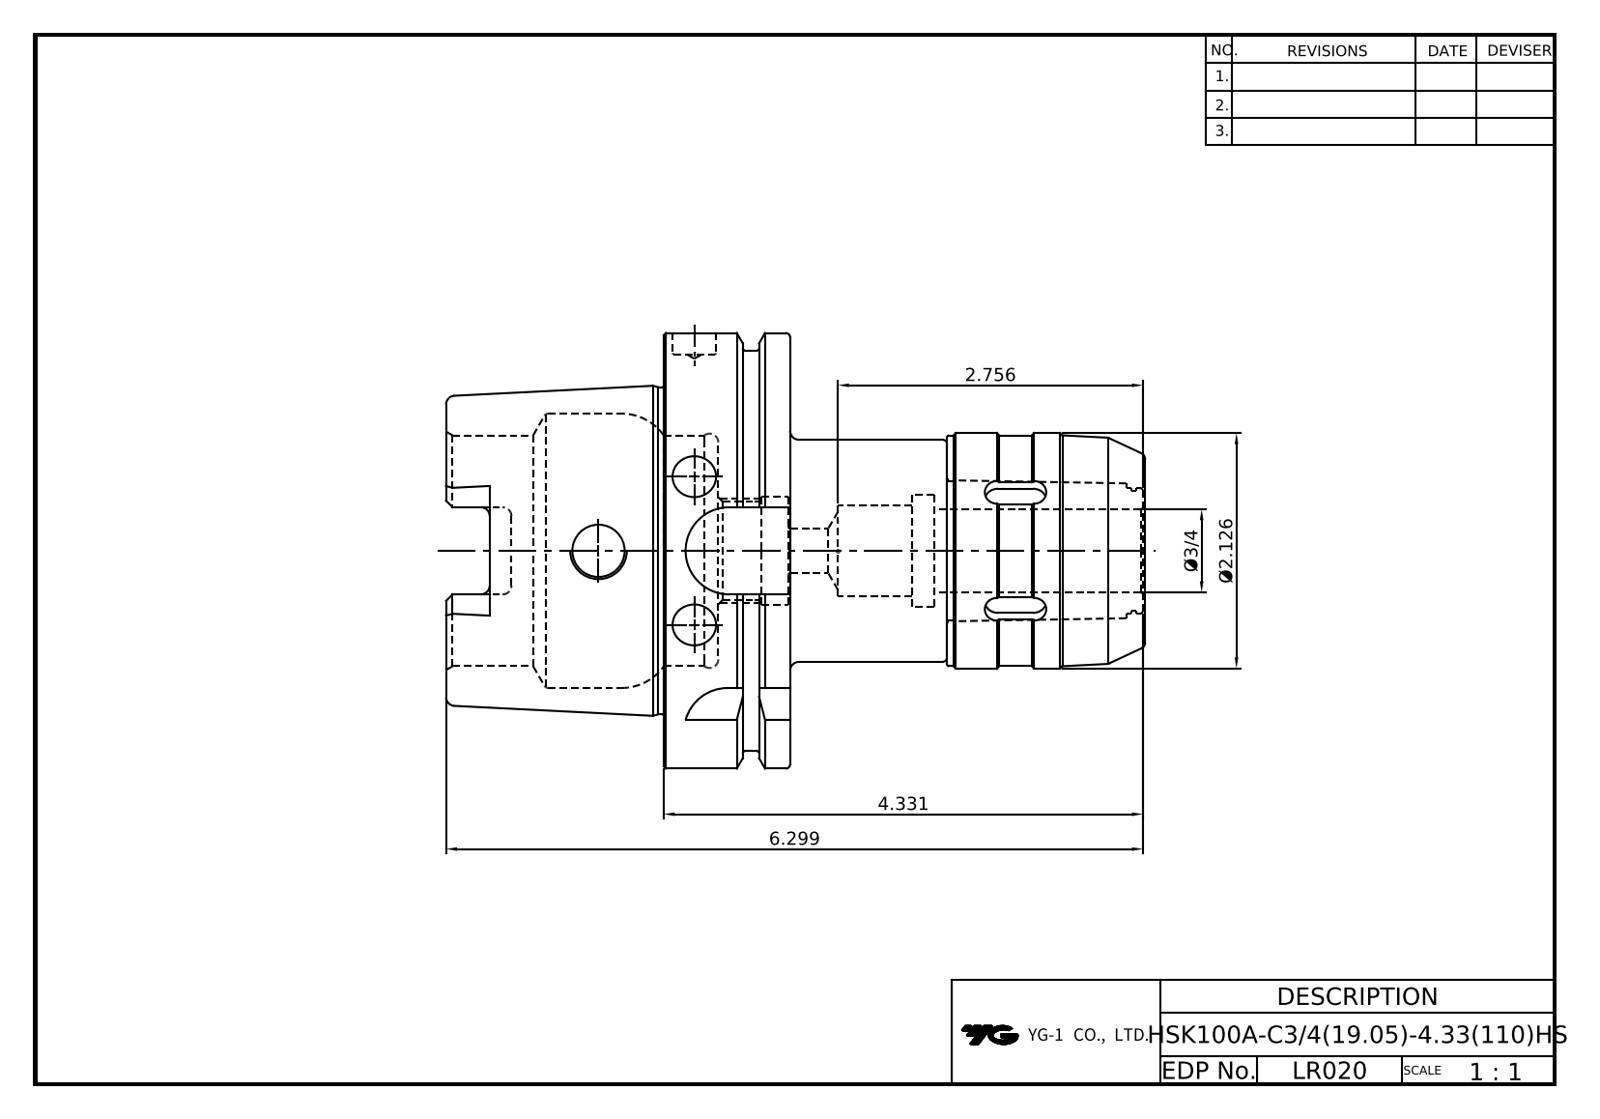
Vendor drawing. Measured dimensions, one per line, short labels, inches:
name: HSK100A-C19.05-110HS; C20-CAP
written by: Autodesk Inventor 2020 (AUTOMOTIVE_DESIGN)
unit: in
bodies: 2 solids, 207 faces (67 planar, 63 cylindrical, 77 other)
size: 6.319 × 3.937 × 3.937
volume: 23.8 in³; area: 124.4 in²
holes: 2× ⌀0.394, 2× ⌀0.472, 1× ⌀0.75, 1× ⌀0.827, 1× ⌀0.881, 1× ⌀0.984, 1× ⌀1.008, 1× ⌀1.539, 1× ⌀1.614, 1× ⌀2.48
bosses: 1× ⌀3.937, 1× ⌀3.622, 1× ⌀2.969, 1× ⌀2.126, 1× ⌀2.087, 1× ⌀2.008, 1× ⌀1.138
rounds: 6× R0.079, 6× R0.118, 4× R0.192, 4× R0.394
face distances: 1.142, 2.559, 1.417, 2.067, 0.492, 0.65, 1.969, 2.461, 3.11, 4.528
